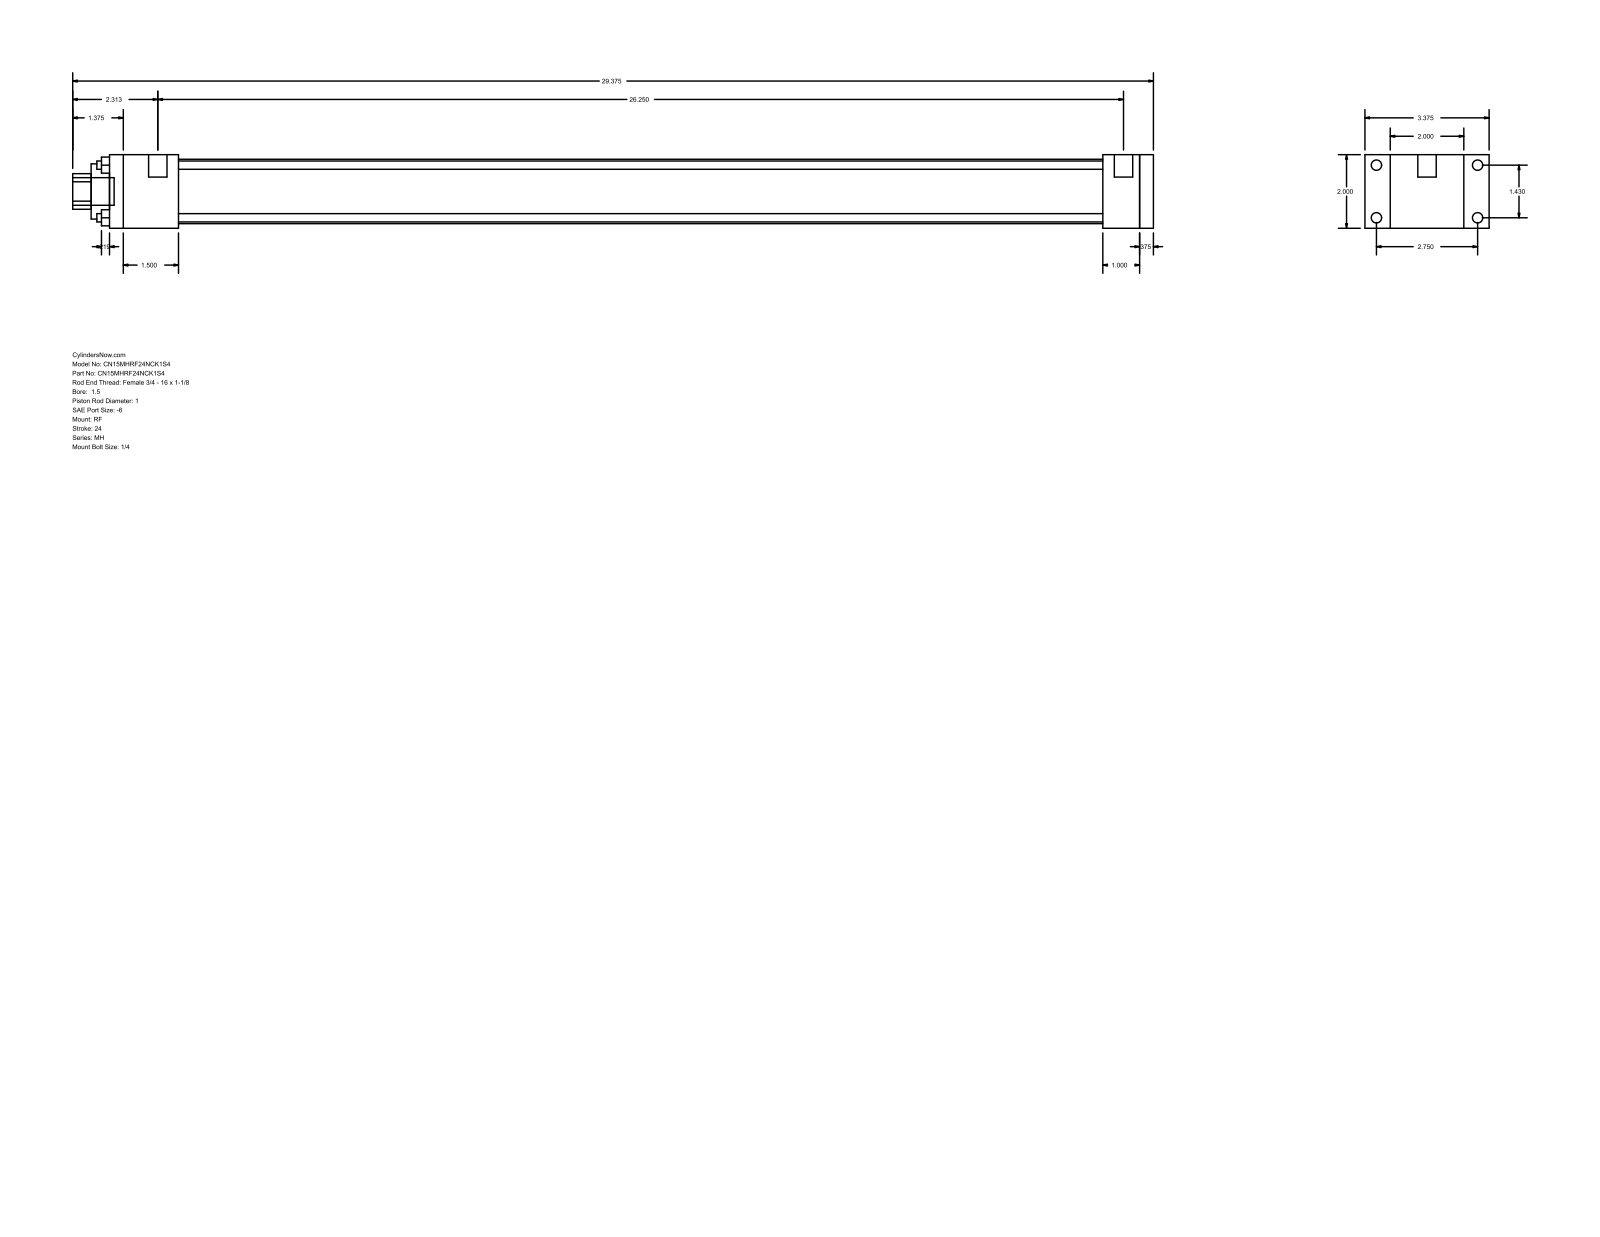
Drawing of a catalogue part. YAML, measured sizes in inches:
part_name: "MH_RF__0150_1"
step_written_by: "GSSL Pune (CONFIG_CONTROL_DESIGN)"
units: inches
bodies: {solids: 0, faces: 92, planar: 64, cylindrical: 28, other: 0}
overall_size: [29.375, 3.375, 2]
round_holes:
  - {diameter: 0.225, count: 4}
  - {diameter: 1, count: 1}
  - {diameter: 1.5, count: 1}
  - {diameter: 1.75, count: 1}
round_bosses_or_shafts:
  - {diameter: 0.281, count: 4}
  - {diameter: 0.219, count: 4}
  - {diameter: 0.5, count: 2}
  - {diameter: 0.75, count: 1}
partial_cylinders:
  - {radius: 0.484, count: 1}
face_to_face_distances: [2, 0.375, 28, 1, 28.375, 0.687, 2.687, 27, 1.375, 1.875]
hole_center_spacings: [1.011, 1.43, 2.022]
